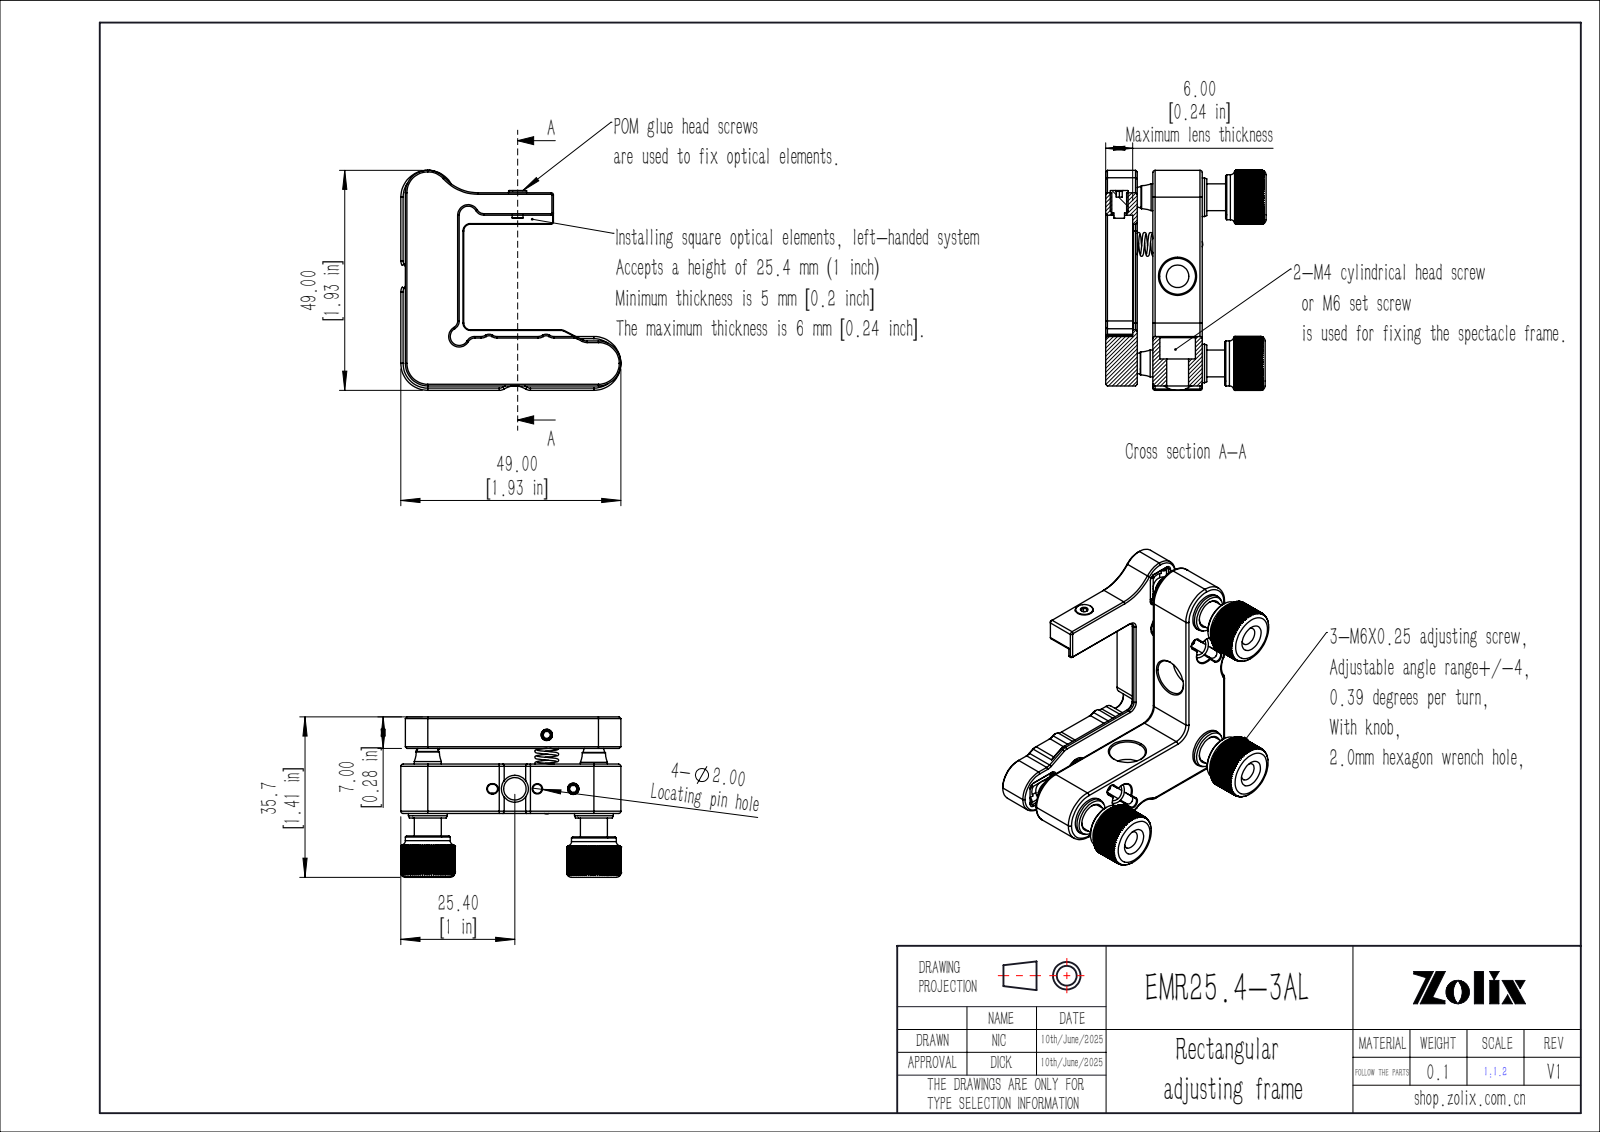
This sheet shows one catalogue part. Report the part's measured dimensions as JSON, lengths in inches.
{"part_name": "EMR25.4-3AL", "step_written_by": "SolidWorks 2020 (CONFIG_CONTROL_DESIGN)", "units": "inches", "bodies": {"solids": 0, "faces": 1241, "planar": 631, "cylindrical": 378, "other": 232}, "overall_size": [1.929, 1.929, 1.406], "round_holes": [[0.236, 4], [0.157, 3], [0.386, 3], [0.079, 2], [0.197, 2], [0.315, 2], [0.13, 1]], "round_bosses_or_shafts": [[0.059, 4], [0.394, 3], [0.339, 3], [0.236, 3], [0.118, 2], [0.079, 2], [0.157, 1], [0.094, 1]], "partial_cylinders_radius": [[0.079, 16], [0.02, 11], [0.031, 8], [0.039, 4], [0.043, 4], [0.059, 4], [0.187, 3], [0.236, 3]], "face_to_face_distances": [0.433, 0.276, 0.039, 0.413, 0.138, 0.472, 0.846, 0.571, 0.323, 0.197], "hole_center_spacings": [0.197, 0.413, 1.043, 1.457, 1.792, 0.512, 0.54, 1.476]}
